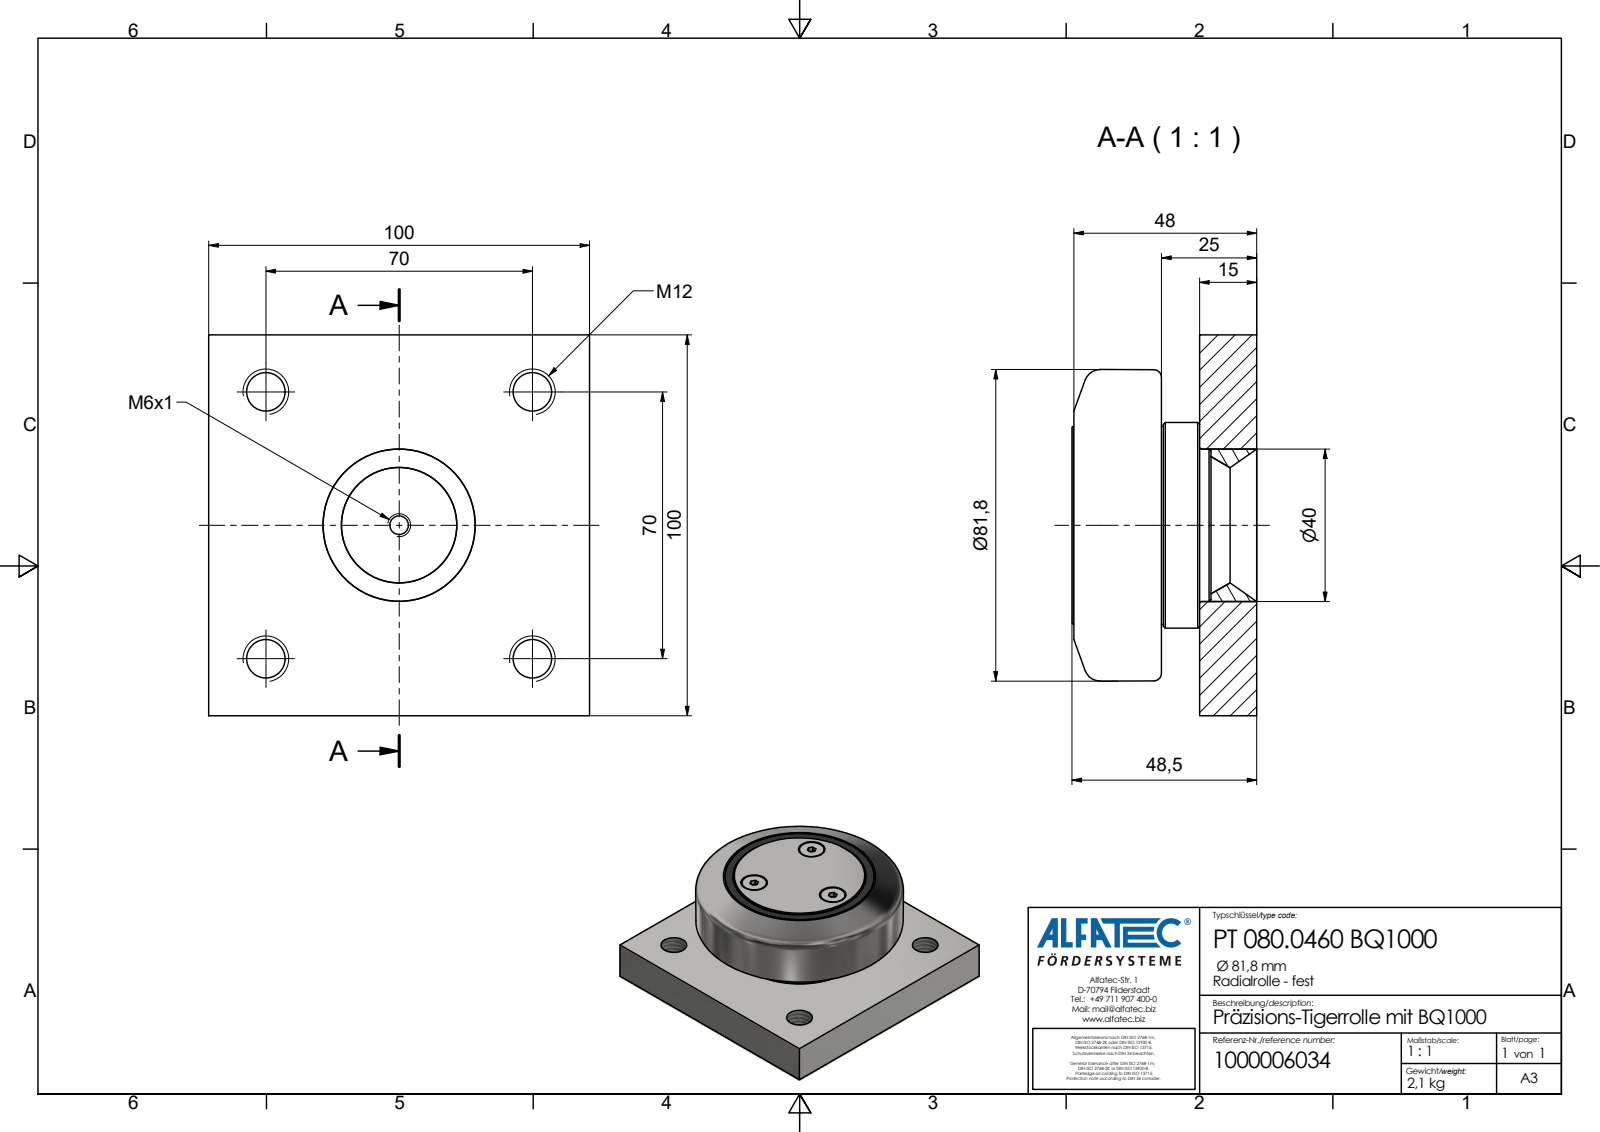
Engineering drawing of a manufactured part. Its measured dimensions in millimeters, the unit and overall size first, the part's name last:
Units: millimetres
Overall size (bounding box): 100 × 100 × 48.5
Round holes (diameter × count): ⌀10.11 ×4, ⌀10.4 ×3, ⌀4.92 ×1
Round bosses / shafts (diameter × count): ⌀9.75 ×3, ⌀54 ×1, ⌀52 ×1
Main face-to-face distances: 15, 100, 25, 10, 23.5, 48.5, 33.5, 0.5, 48, 33
Hole centre spacings: 49.5, 70, 18.5, 32.04, 31.99, 38.69, 48.15, 57.15
Volume: 276 938 mm³ · Surface area: 40 734 mm²
Bodies: 1 solid, 61 faces (39 planar, 14 cylindrical, 8 other)
Part name (STEP PRODUCT): PT 080.0460 BQ1000_Kontur
STEP written by: Autodesk Inventor 2020 (AP242_MANAGED_MODEL_BASED_3D_ENGINEERING_MIM_LF)
